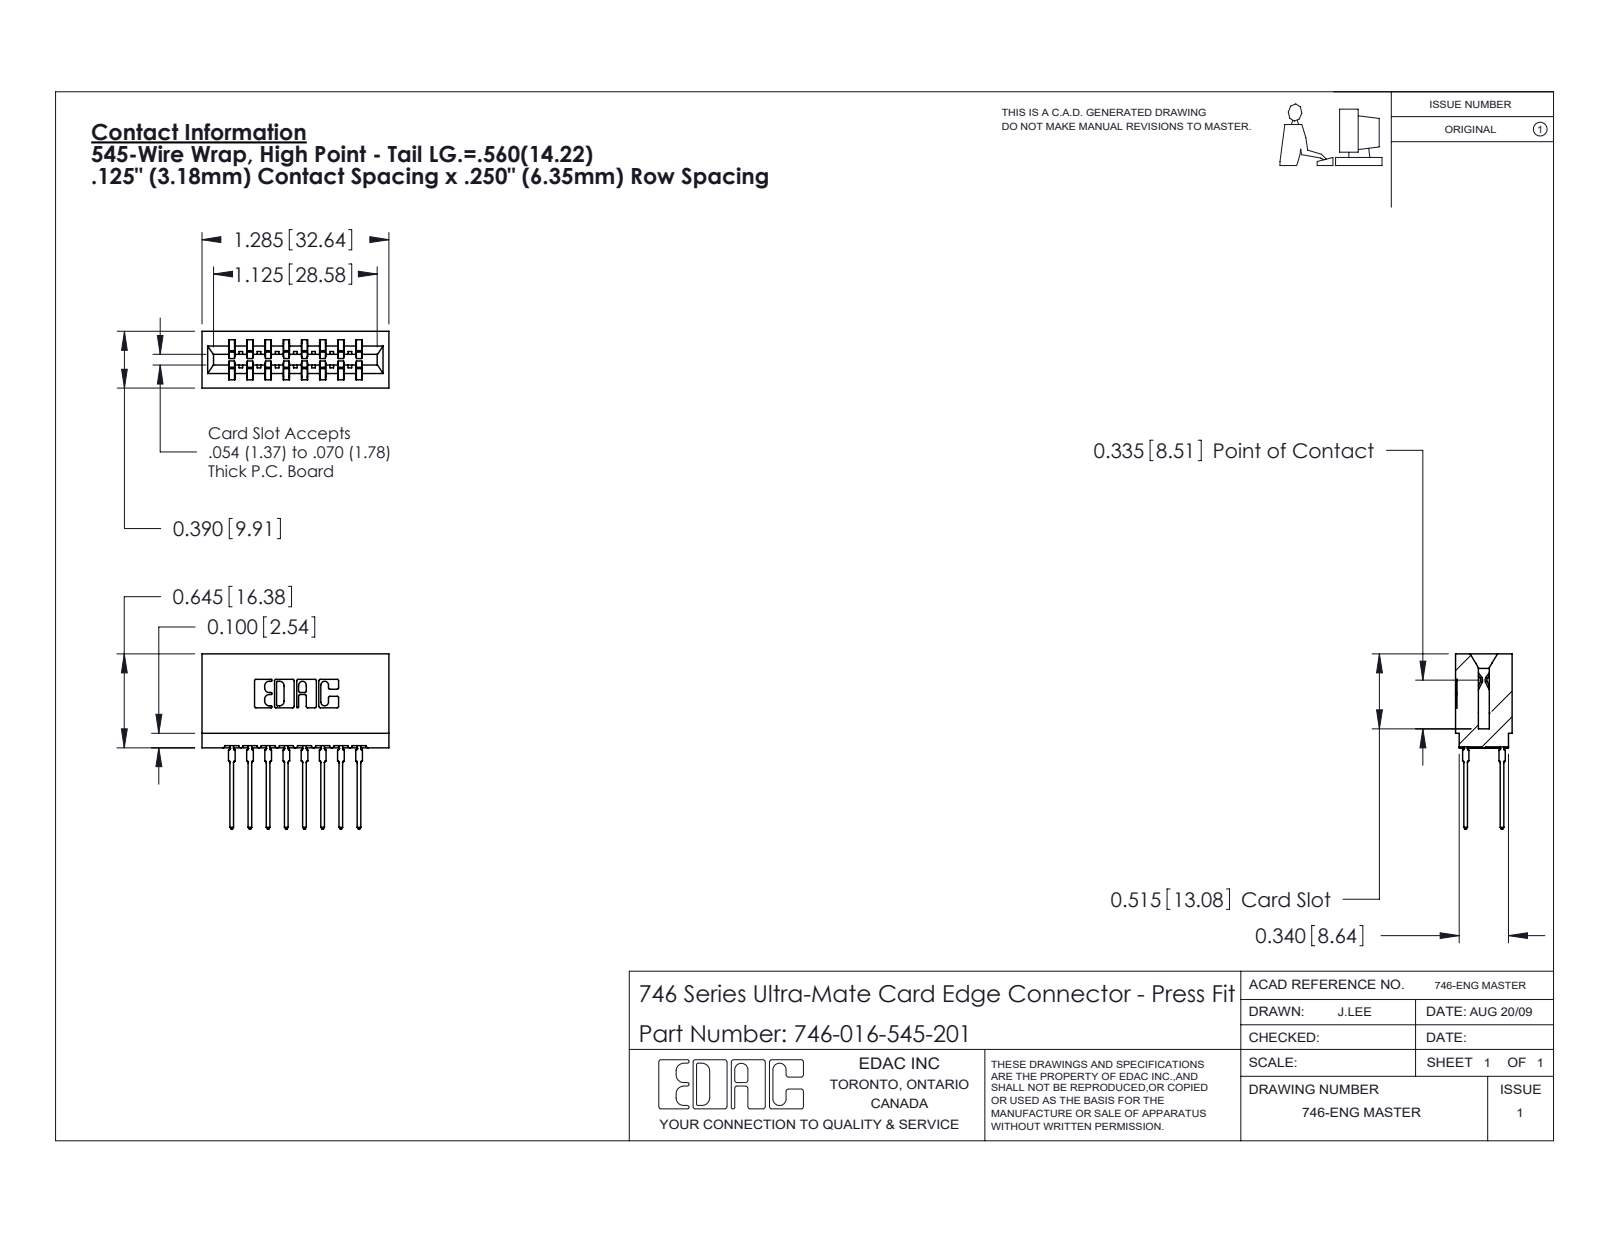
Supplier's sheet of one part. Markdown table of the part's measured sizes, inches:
| quantity | value |
| --- | --- |
| part name | 746 Part_.515 Slot Depth - 01; 746-016-545-201; 746-292-001_545 |
| STEP written by | SolidWorks 2020 (CONFIG_CONTROL_DESIGN) |
| units | inches |
| bodies | 17 solids, 1529 faces (791 planar, 322 cylindrical, 416 other) |
| overall size | 1.285 × 1.204 × 0.39 |
| volume | 0.23 in³ |
| surface area | 8.729 in² |
| partial cylindrical surfaces (radius × count) | 0.021 × 32, 0.01 × 22, 0.015 × 9, 0.005 × 8, 0.011 × 8, 0.007 × 6, 0.031 × 6, 0.026 × 3 |
| main face-to-face distances | 0.25, 0.333, 0.057, 0.042, 0.125, 0.5, 0.292, 0.208, 0.375, 0.125 |
